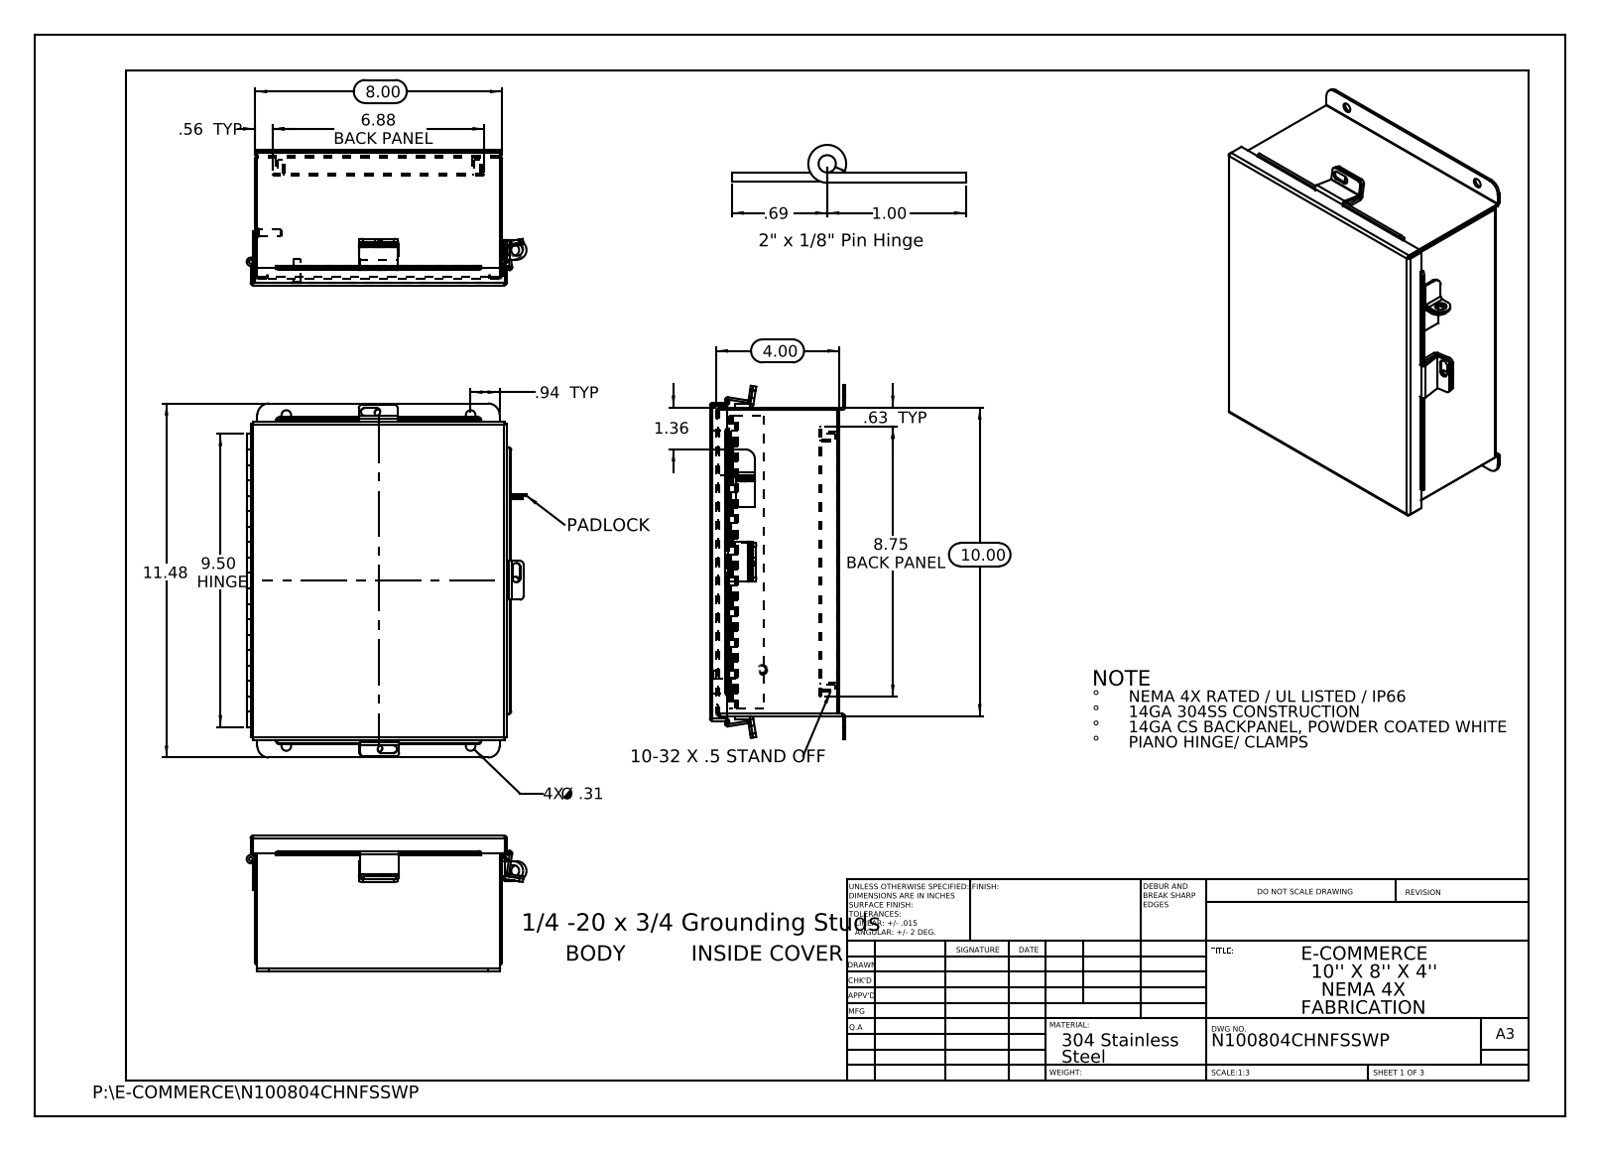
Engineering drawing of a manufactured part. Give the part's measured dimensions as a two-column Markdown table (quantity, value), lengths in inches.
| quantity | value |
| --- | --- |
| part name | N100804CHNFSSWP Hinge Cover Side JIC; N100804CHNFSSWP _JIC Hinge; N100804CHNFSSWP JIC Bottom; N100804CHNFSSWP JIC Clamp Bracket (+8 more) |
| STEP written by | SolidWorks 2013 (CONFIG_CONTROL_DESIGN) |
| units | inches |
| bodies | 21 solids, 620 faces (383 planar, 217 cylindrical, 20 other) |
| overall size | 11.476 × 9.072 × 4.39 |
| volume | 32.93 in³ |
| surface area | 904.4 in² |
| round holes (diameter × count) | 0.25 × 7, 0.187 × 4, 0.312 × 4, 0.125 × 1, 0.373 × 1, 0.375 × 1 |
| round bosses / shafts (diameter × count) | 0.313 × 4, 0.315 × 2, 0.236 × 2, 0.273 × 1, 0.25 × 1 |
| partial cylindrical surfaces (radius × count) | 0.013 × 13, 0.009 × 12, 0.088 × 12, 0.125 × 10, 0.083 × 6, 0.1 × 6, 0.133 × 6, 0.375 × 4 |
| main face-to-face distances | 0.075, 4.128, 4.053, 4.203, 7.925, 9.925, 0.074, 0.575, 0.5, 3.553 |
| hole center spacings | 1.315, 6.311, 9.428, 11.269, 5.976, 6.375, 8.126, 10.328 |
